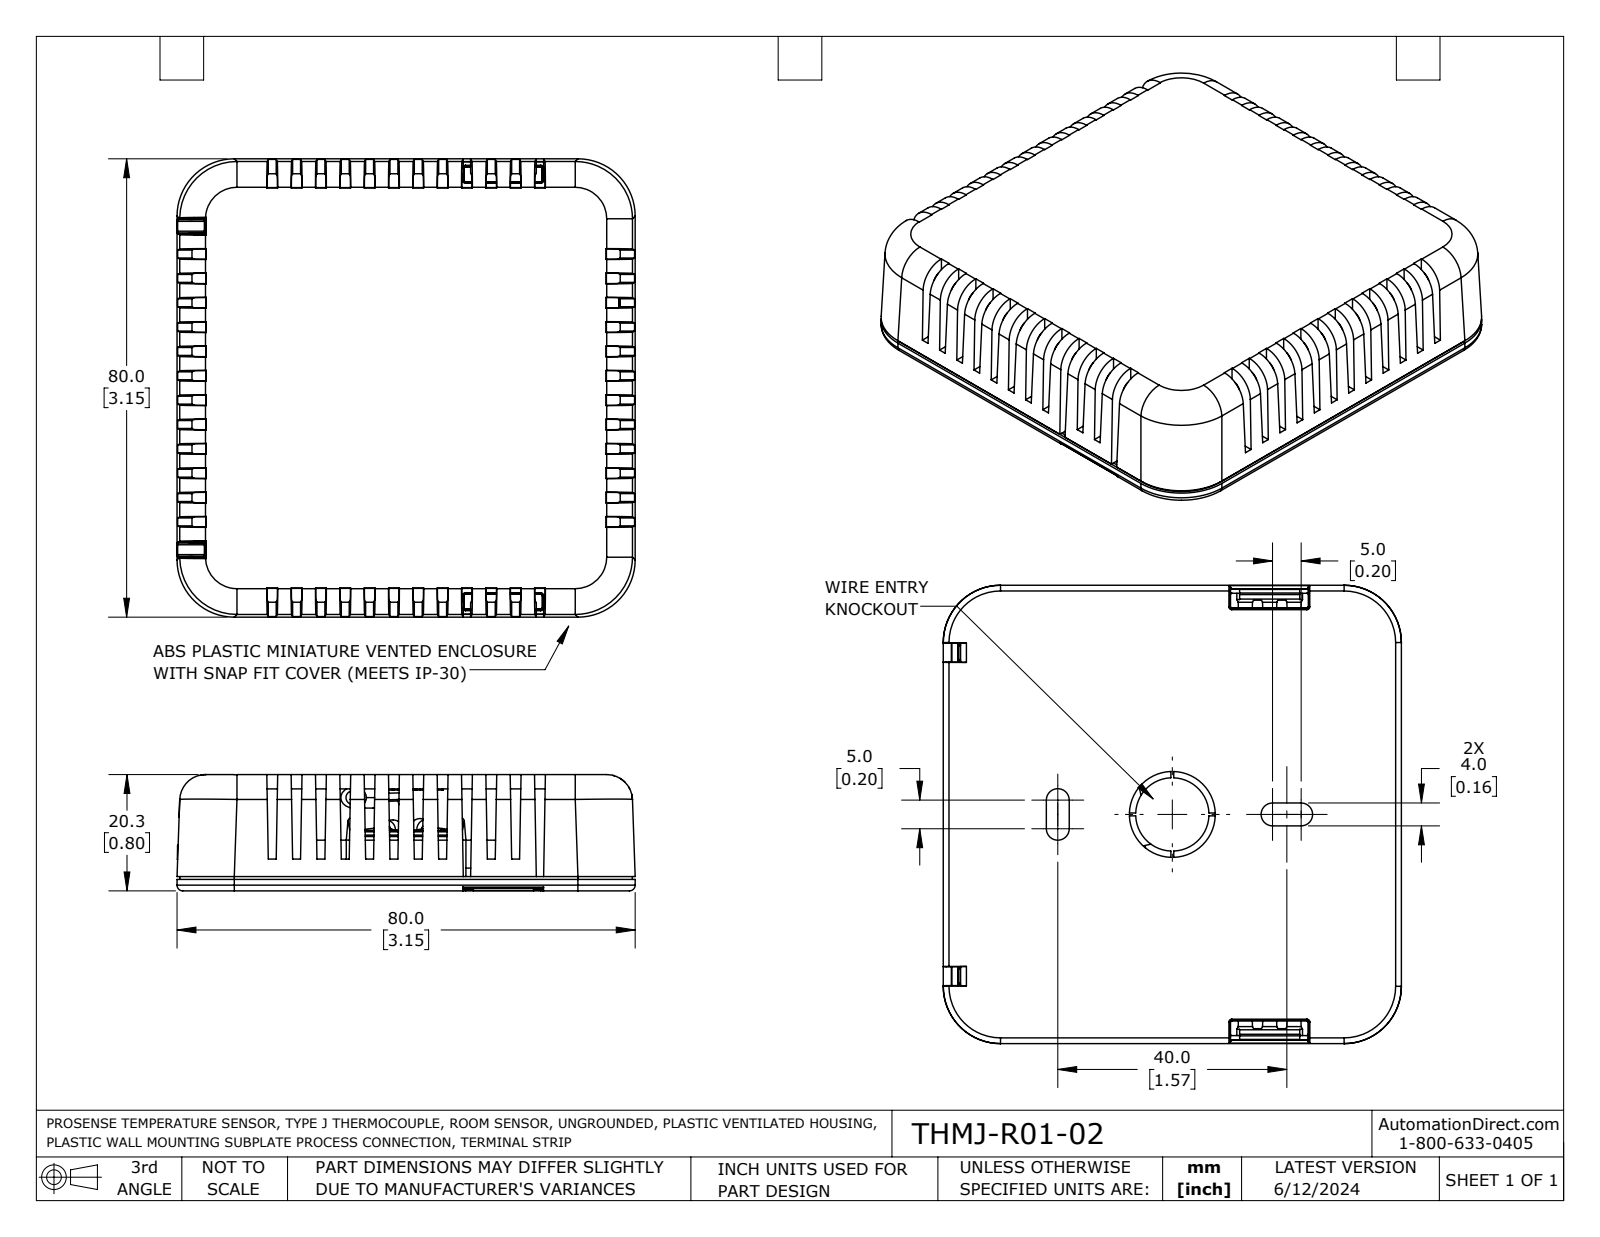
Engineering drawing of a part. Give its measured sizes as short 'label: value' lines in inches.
name: THMJ-R01-02
written by: SolidWorks 2021 (AUTOMOTIVE_DESIGN)
unit: in
bodies: 15 solids, 1372 faces (792 planar, 313 cylindrical, 267 other)
size: 3.15 × 3.15 × 0.799
volume: 2.542 in³; area: 66.18 in²
holes: 8× ⌀0.217, 6× ⌀0.175, 4× ⌀0.098, 2× ⌀0.07, 2× ⌀0.146, 2× ⌀0.175
bosses: 4× ⌀0.27, 4× ⌀0.17, 4× ⌀0.12, 2× ⌀0.138, 2× ⌀0.045, 2× ⌀0.045, 2× ⌀0.01
rounds: 24× R0.01, 16× R0.012, 9× R0.037, 9× R0.038, 8× R0.145, 8× R0.394, 6× R0.03, 5× R0.039
face distances: 0.098, 0.701, 0.799, 0.602, 0.167, 0.335, 0.502, 0.669, 0.837, 1.004
hole spacings: 0.3, 0.374, 0.479, 0.748, 0.806, 0.374, 0.48, 1.121
